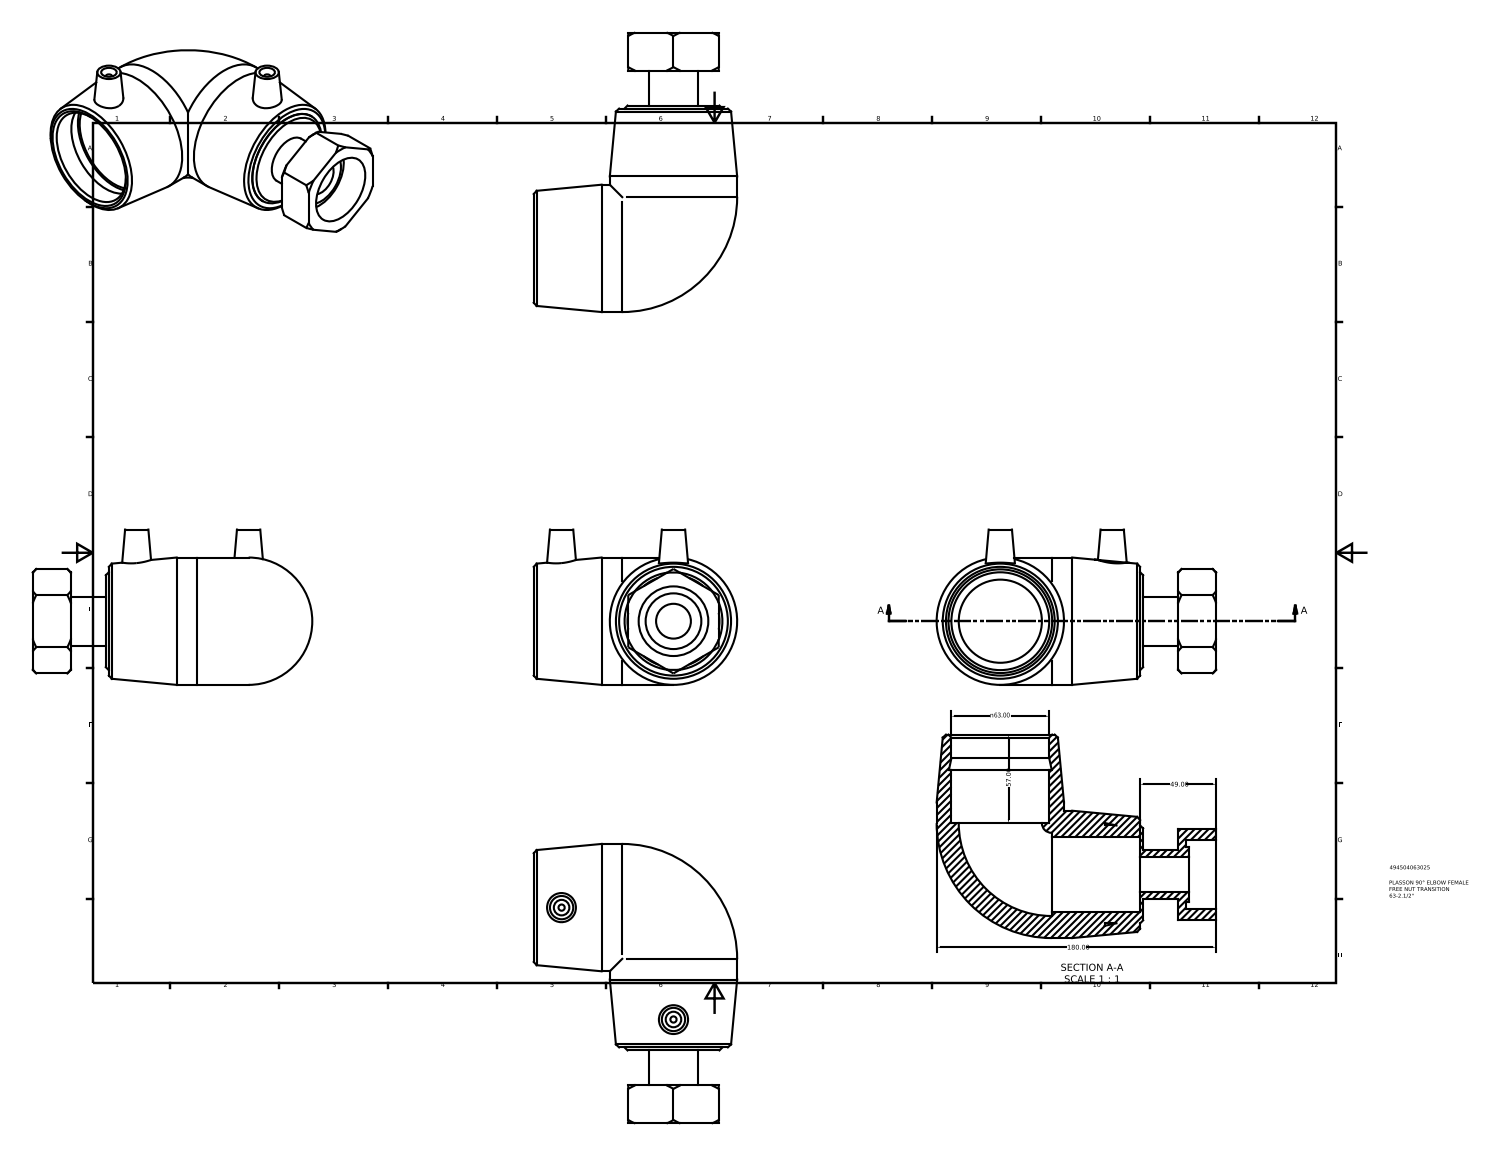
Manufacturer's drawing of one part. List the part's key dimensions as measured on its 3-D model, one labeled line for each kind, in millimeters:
Part name (STEP PRODUCT): 494504063025
STEP written by: Autodesk Inventor 2015 (AUTOMOTIVE_DESIGN)
Units: millimetres
Bodies: 1 solid, 63 faces (24 planar, 15 cylindrical, 24 other)
Overall size (bounding box): 180 × 131 × 100
Volume: 494 660 mm³ · Surface area: 101 040 mm²
Round holes (diameter × count): ⌀10 ×2, ⌀22.42 ×1, ⌀44.84 ×1, ⌀48 ×1, ⌀63 ×1
Round bosses / shafts (diameter × count): ⌀82 ×2, ⌀4 ×2, ⌀63 ×1, ⌀35.88 ×1, ⌀31.39 ×1
Main face-to-face distances: 24.5, 1.96, 58.26, 22.54, 49, 47.04, 29.4, 3.87, 62.13, 57
Hole centre spacings: 101.89
